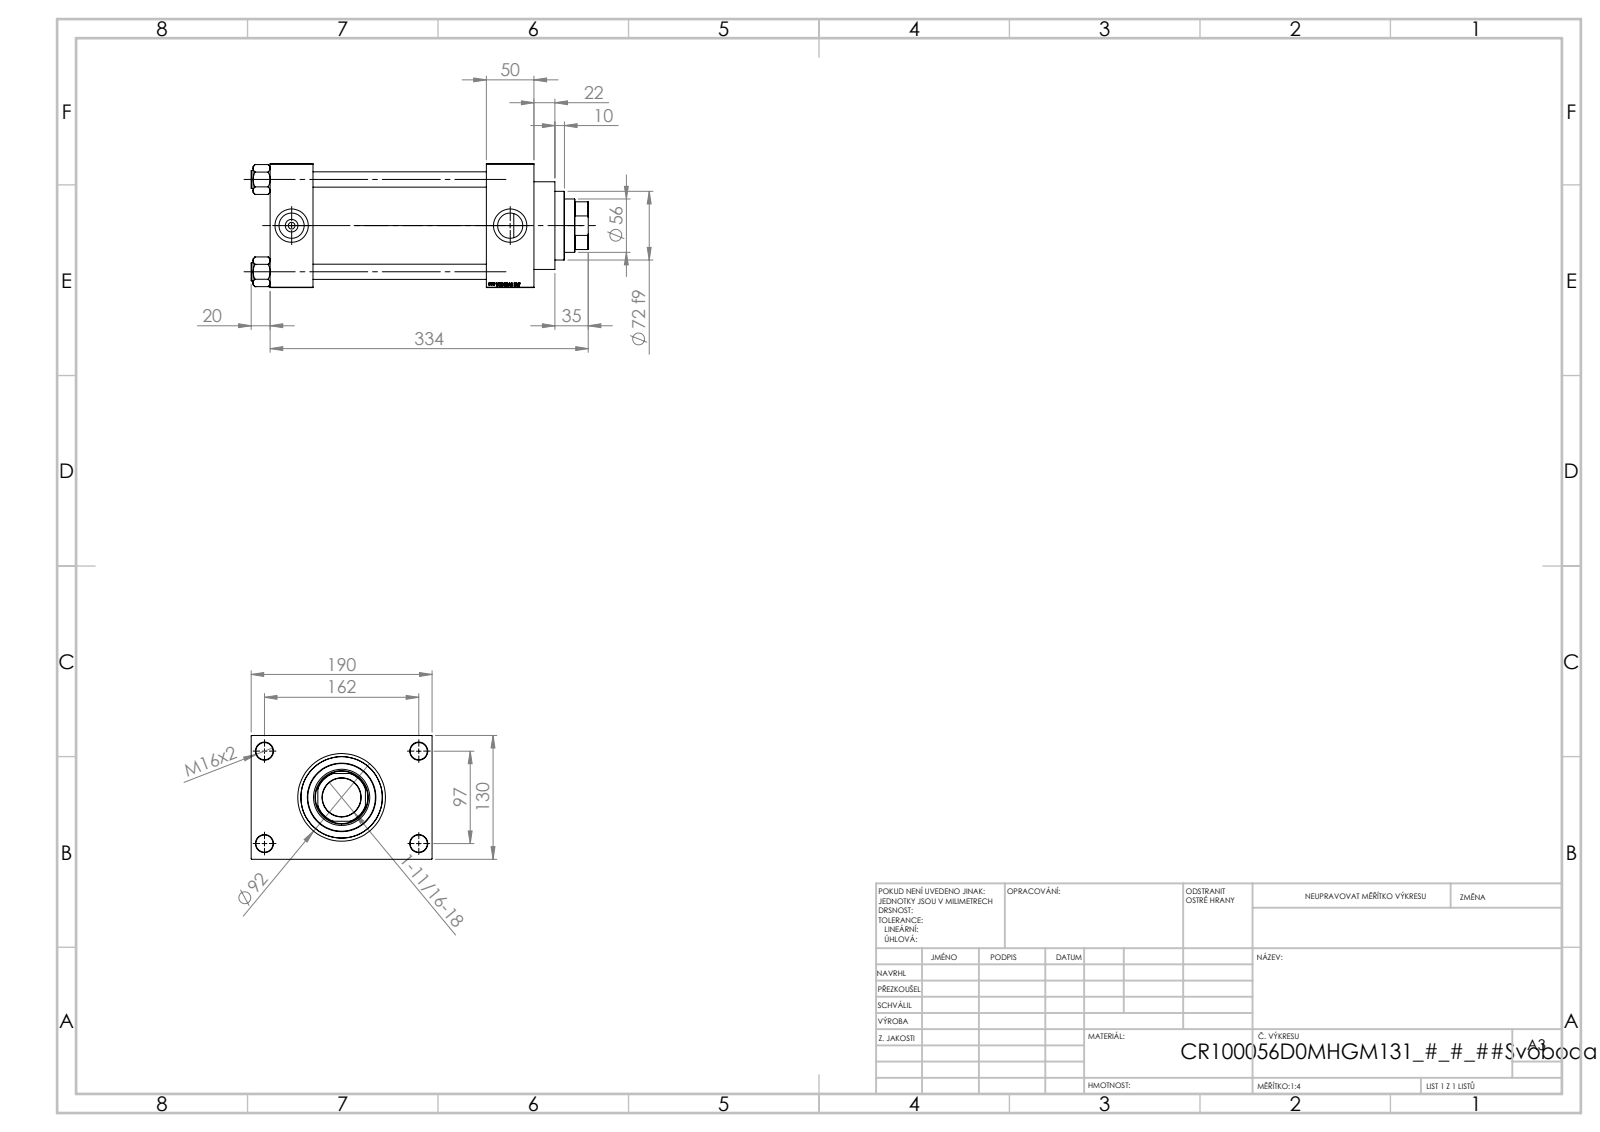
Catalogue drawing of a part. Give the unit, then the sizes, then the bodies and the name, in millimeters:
Units: millimetres
Overall size (bounding box): 354 × 190 × 130
Round holes (diameter × count): ⌀16 ×4, ⌀18 ×4, ⌀7 ×2, ⌀26.44 ×2, ⌀35 ×2, ⌀40.5 ×1, ⌀56 ×1, ⌀59 ×1, ⌀76 ×1, ⌀85.5 ×1, ⌀100 ×1
Round bosses / shafts (diameter × count): ⌀19 ×4, ⌀106 ×1, ⌀92 ×1, ⌀72 ×1
Partial cylindrical surfaces — rounded edges, fillets, slot ends (radius × count): R27 ×1
Main face-to-face distances: 130, 50, 45, 227, 182, 277, 232, 30, 160, 190
Hole centre spacings: 32.55, 68.52, 94.41, 96.9, 102.27, 129.45, 161.73, 97
Volume: 3 098 000 mm³ · Surface area: 476 045 mm²
Bodies: 11 solids, 1151 faces (545 planar, 88 cylindrical, 518 other)
Part name (STEP PRODUCT): V215CR_D_Body; V215CR_D_TYCINKA; V215CR_VCP_D; V215_VC_A (+1 more)
STEP written by: SolidWorks 2019 (CONFIG_CONTROL_DESIGN)
